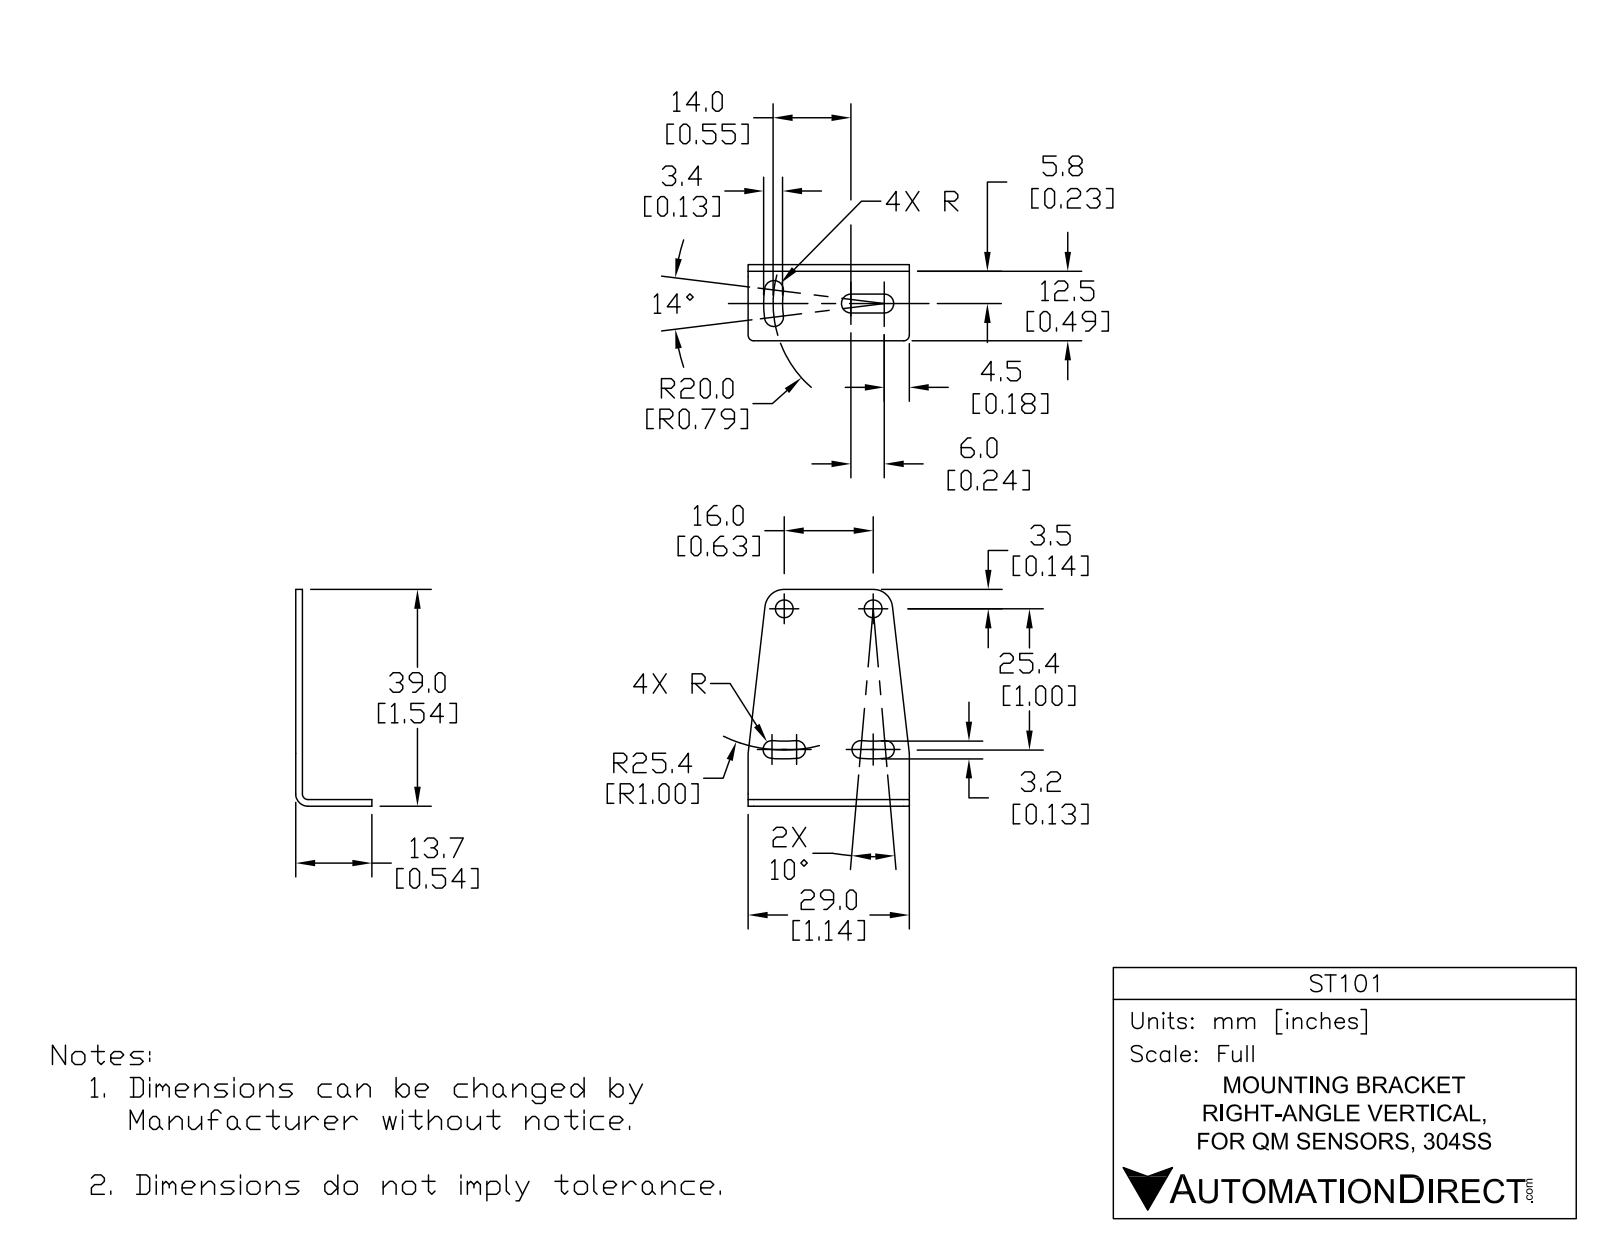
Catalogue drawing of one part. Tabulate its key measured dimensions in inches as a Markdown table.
| quantity | value |
| --- | --- |
| part name | ST101 |
| STEP written by | SolidWorks 2017 (AUTOMOTIVE_DESIGN) |
| units | inches |
| bodies | 1 solid, 43 faces (12 planar, 31 cylindrical, 0 other) |
| overall size | 1.535 × 1.142 × 0.539 |
| volume | 0.092 in³ |
| surface area | 4.366 in² |
| round holes (diameter × count) | 0.126 × 2 |
| partial cylindrical surfaces (radius × count) | 0.063 × 4, 0.067 × 4, 0.039 × 3, 0.138 × 2, 0.946 × 2, 1.072 × 2, 0.087 × 1, 0.72 × 1 |
| main face-to-face distances | 0.047, 0.492, 0.539, 1.142, 1.535, 1.488, 0.331, 0.161, 0.209, 0.197 |
| hole center spacings | 0.63 |
